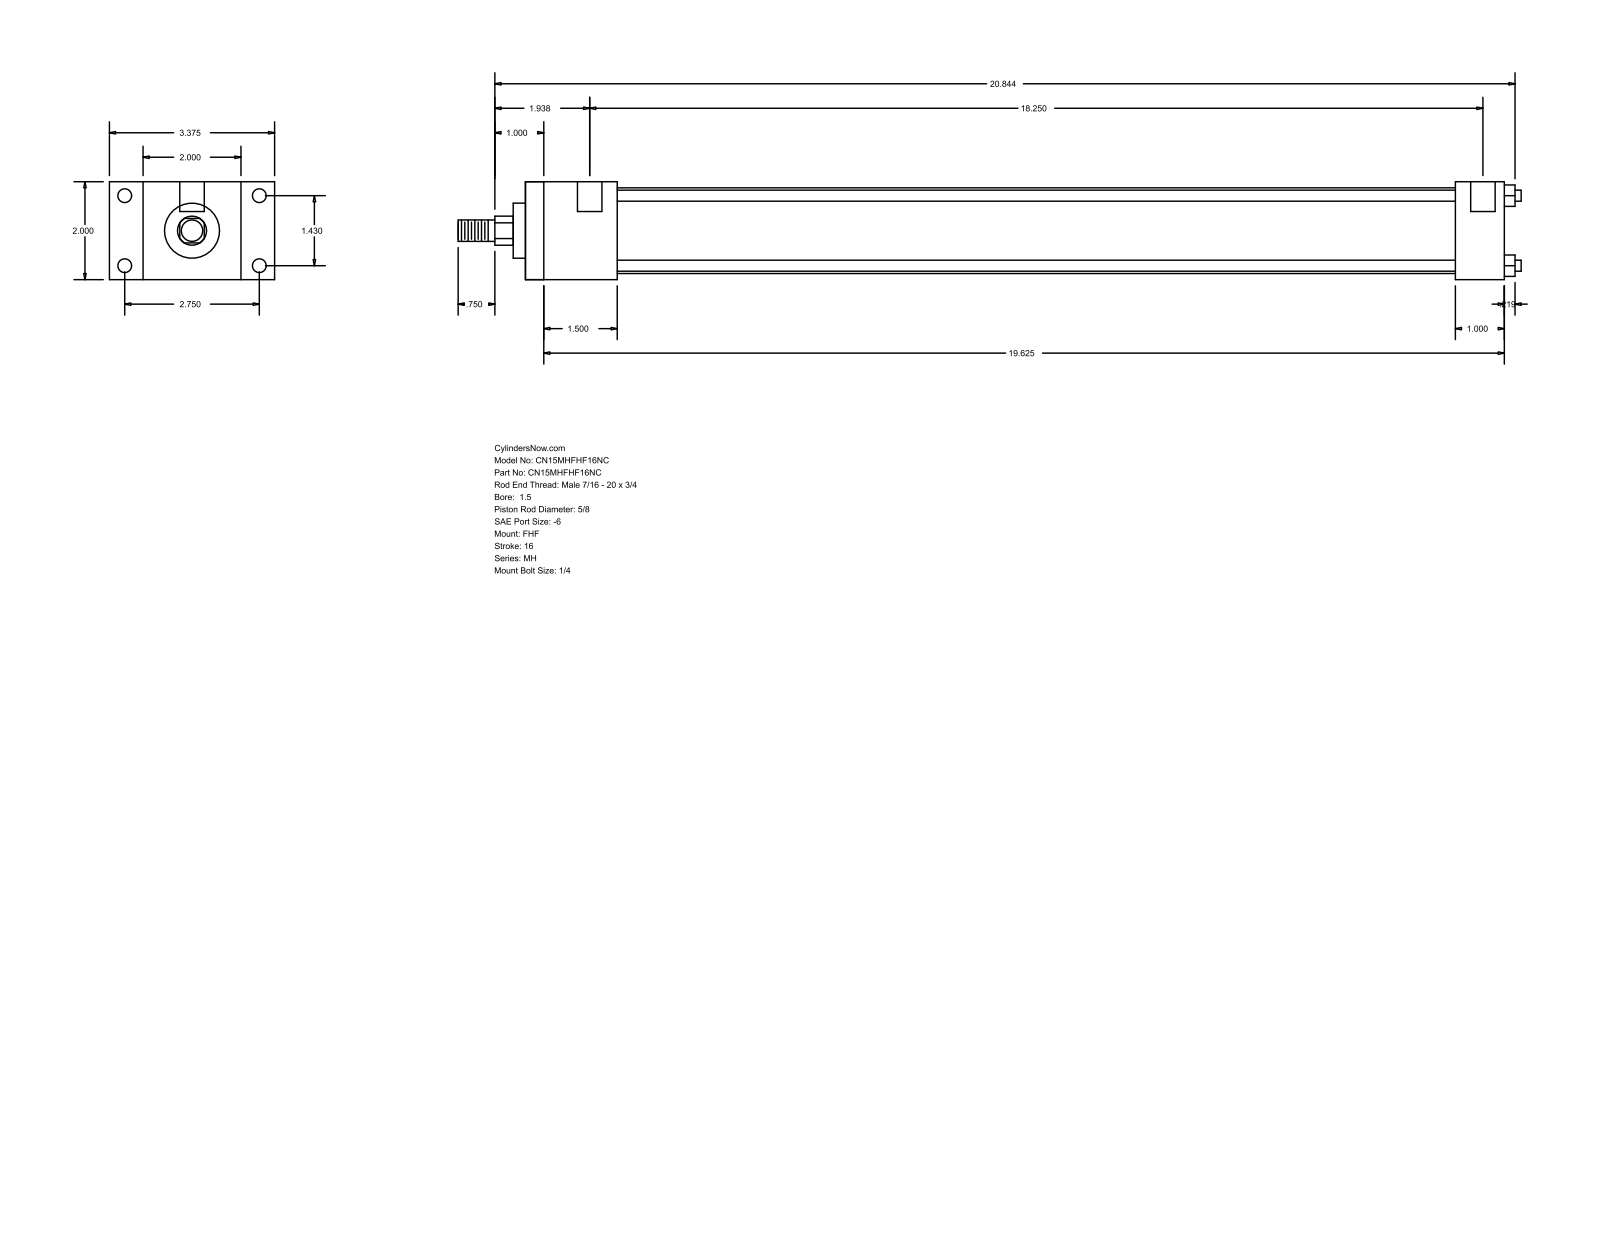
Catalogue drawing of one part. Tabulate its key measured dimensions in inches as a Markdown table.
| quantity | value |
| --- | --- |
| part name | MH_FHF__0150_0.625 |
| STEP written by | GSSL Pune (CONFIG_CONTROL_DESIGN) |
| units | inches |
| bodies | 0 solids, 88 faces (60 planar, 28 cylindrical, 0 other) |
| overall size | 21.719 × 3.375 × 2 |
| round holes (diameter × count) | 0.219 × 4, 0.281 × 4, 0.5 × 2 |
| round bosses / shafts (diameter × count) | 0.225 × 4, 1.75 × 1, 1.125 × 1, 0.625 × 1, 0.437 × 1 |
| partial cylindrical surfaces (radius × count) | 0.297 × 1 |
| main face-to-face distances | 2, 0.687, 2.687, 1.875, 3.375, 20, 18.125, 1, 19, 17.125 |
| hole center spacings | 1.43, 2.75, 3.099, 18.375, 0.125, 18.25 |
